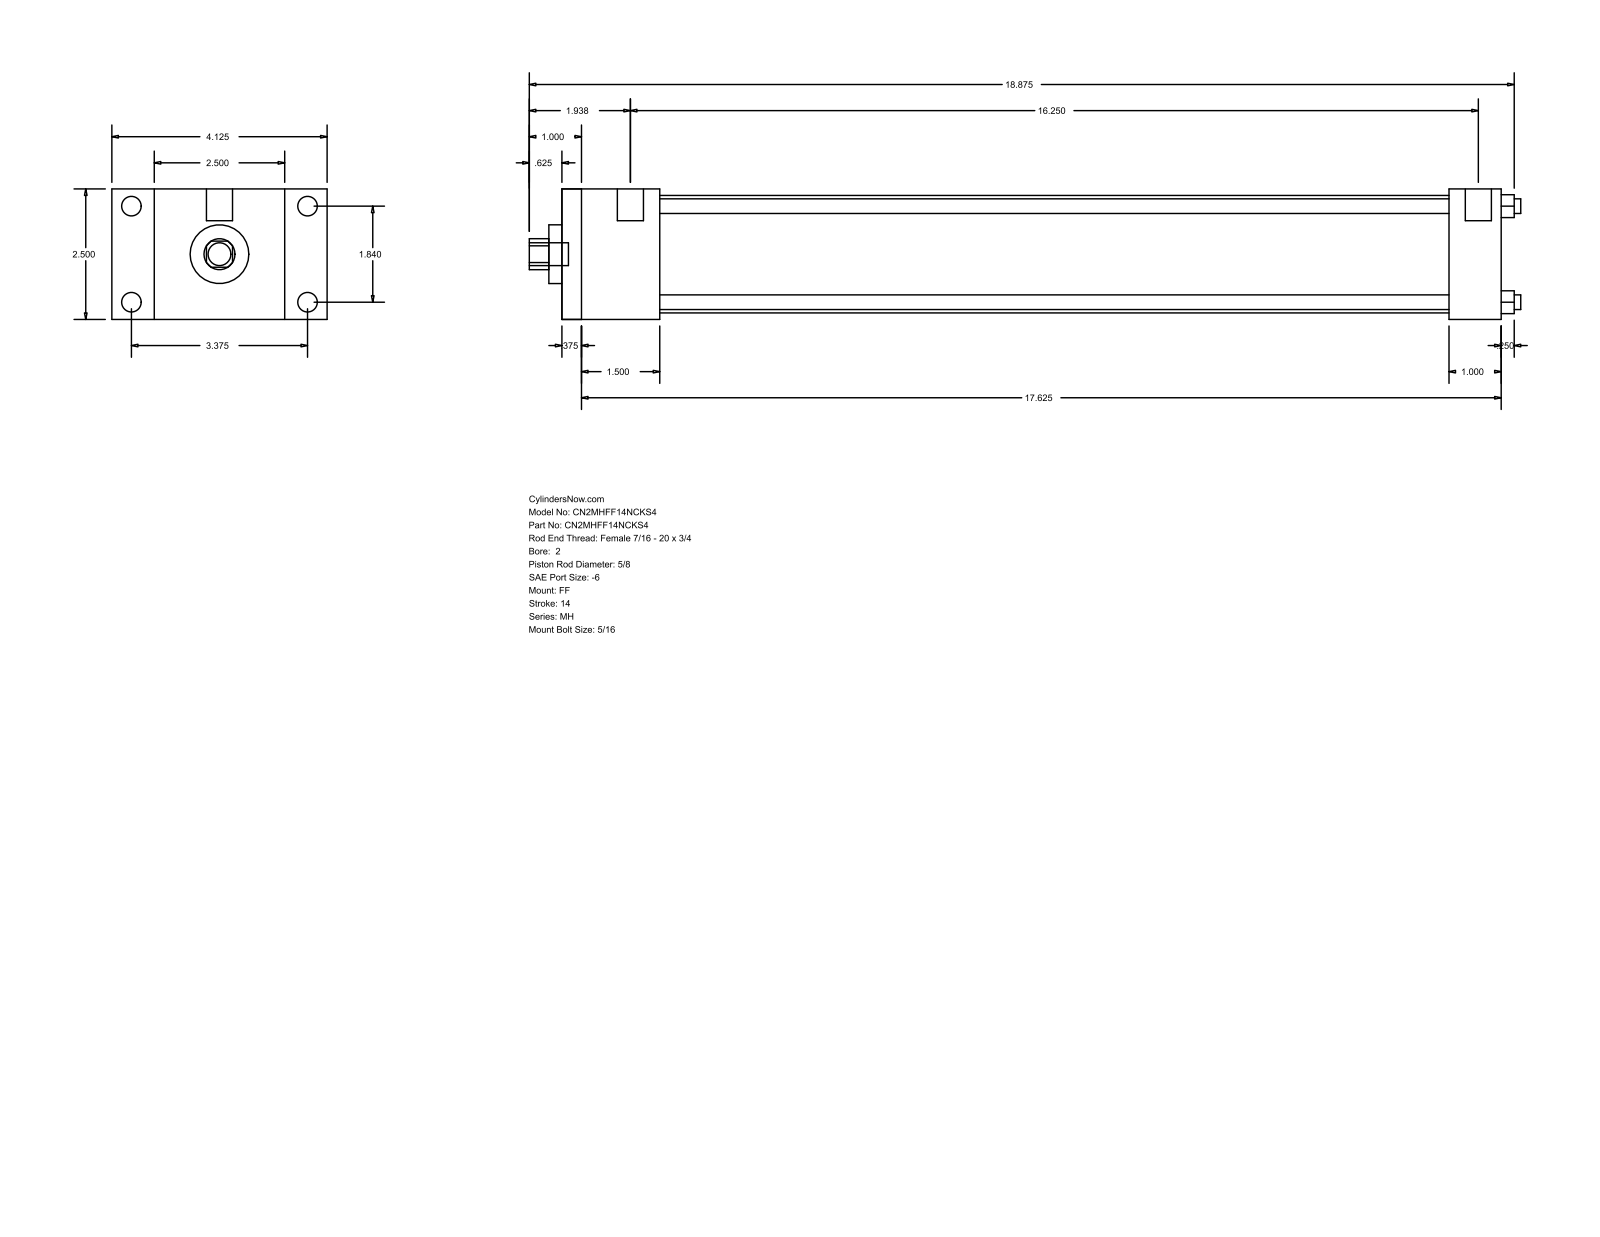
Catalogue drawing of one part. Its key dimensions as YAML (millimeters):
part_name: "MH_FF__0200_0.625"
step_written_by: "GSSL Pune (CONFIG_CONTROL_DESIGN)"
units: millimeters
bodies: {solids: 0, faces: 92, planar: 64, cylindrical: 28, other: 0}
overall_size: [482.6, 104.78, 63.5]
round_holes:
  - {diameter: 7.14, count: 4}
  - {diameter: 15.88, count: 1}
  - {diameter: 28.57, count: 1}
  - {diameter: 57.15, count: 1}
round_bosses_or_shafts:
  - {diameter: 9.53, count: 4}
  - {diameter: 5.56, count: 4}
  - {diameter: 12.7, count: 2}
  - {diameter: 11.11, count: 1}
partial_cylinders:
  - {radius: 7.54, count: 1}
face_to_face_distances: [63.5, 457.19, 9.52, 447.67, 38.1, 47.62, 431.8, 422.28, 384.18, 409.57]
hole_center_spacings: [33.05, 46.74, 66.1]
